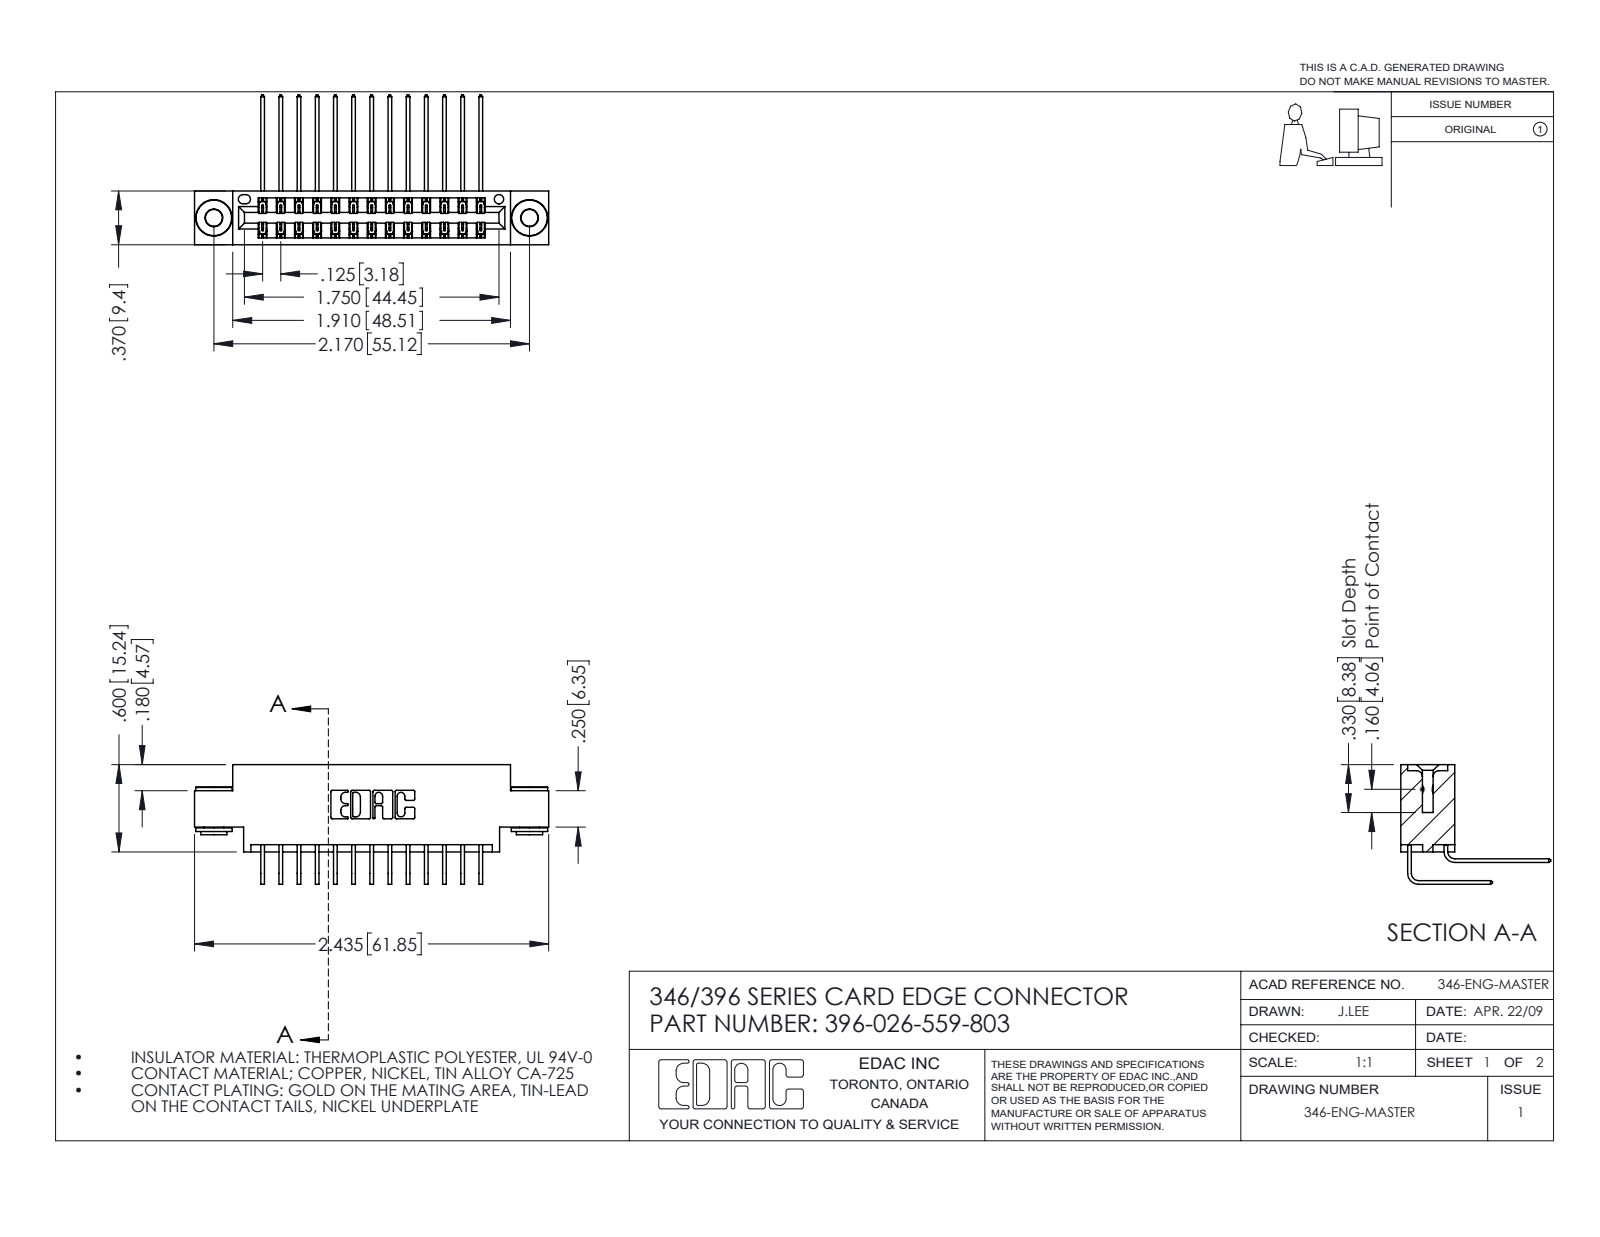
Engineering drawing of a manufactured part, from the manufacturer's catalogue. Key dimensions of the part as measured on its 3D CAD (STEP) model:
Part name (STEP PRODUCT): 396-026-559-803; 345-292-001_558 559 Tail - 1; 345-250-002_345-250-002-102; 346 Part_0.170 Offset - 0.156 Dia-TH (+1 more)
STEP written by: SolidWorks 2016 (CONFIG_CONTROL_DESIGN)
Units: inches
Bodies: 29 solids, 1568 faces (1052 planar, 508 cylindrical, 8 other)
Overall size (bounding box): 2.435 × 1.03 × 0.823
Volume: 0.355 in³ · Surface area: 13.42 in²
Round holes (diameter × count): ⌀0.116 ×2, ⌀0.156 ×2, ⌀0.064 ×1
Round bosses / shafts (diameter × count): ⌀0.25 ×2, ⌀0.18 ×2, ⌀0.136 ×2
Partial cylindrical surfaces — rounded edges, fillets, slot ends (radius × count): R0.006 ×39, R0.01 ×22, R0.007 ×6, R0.031 ×6, R0.026 ×3, R0.014 ×2, R0.022 ×2, R0.024 ×2
Main face-to-face distances: 0.048, 0.25, 0.322, 0.37, 0.025, 0.072, 0.298, 0.275, 0.15, 0.148
Hole centre spacings: 0.246, 1.964, 2.17
